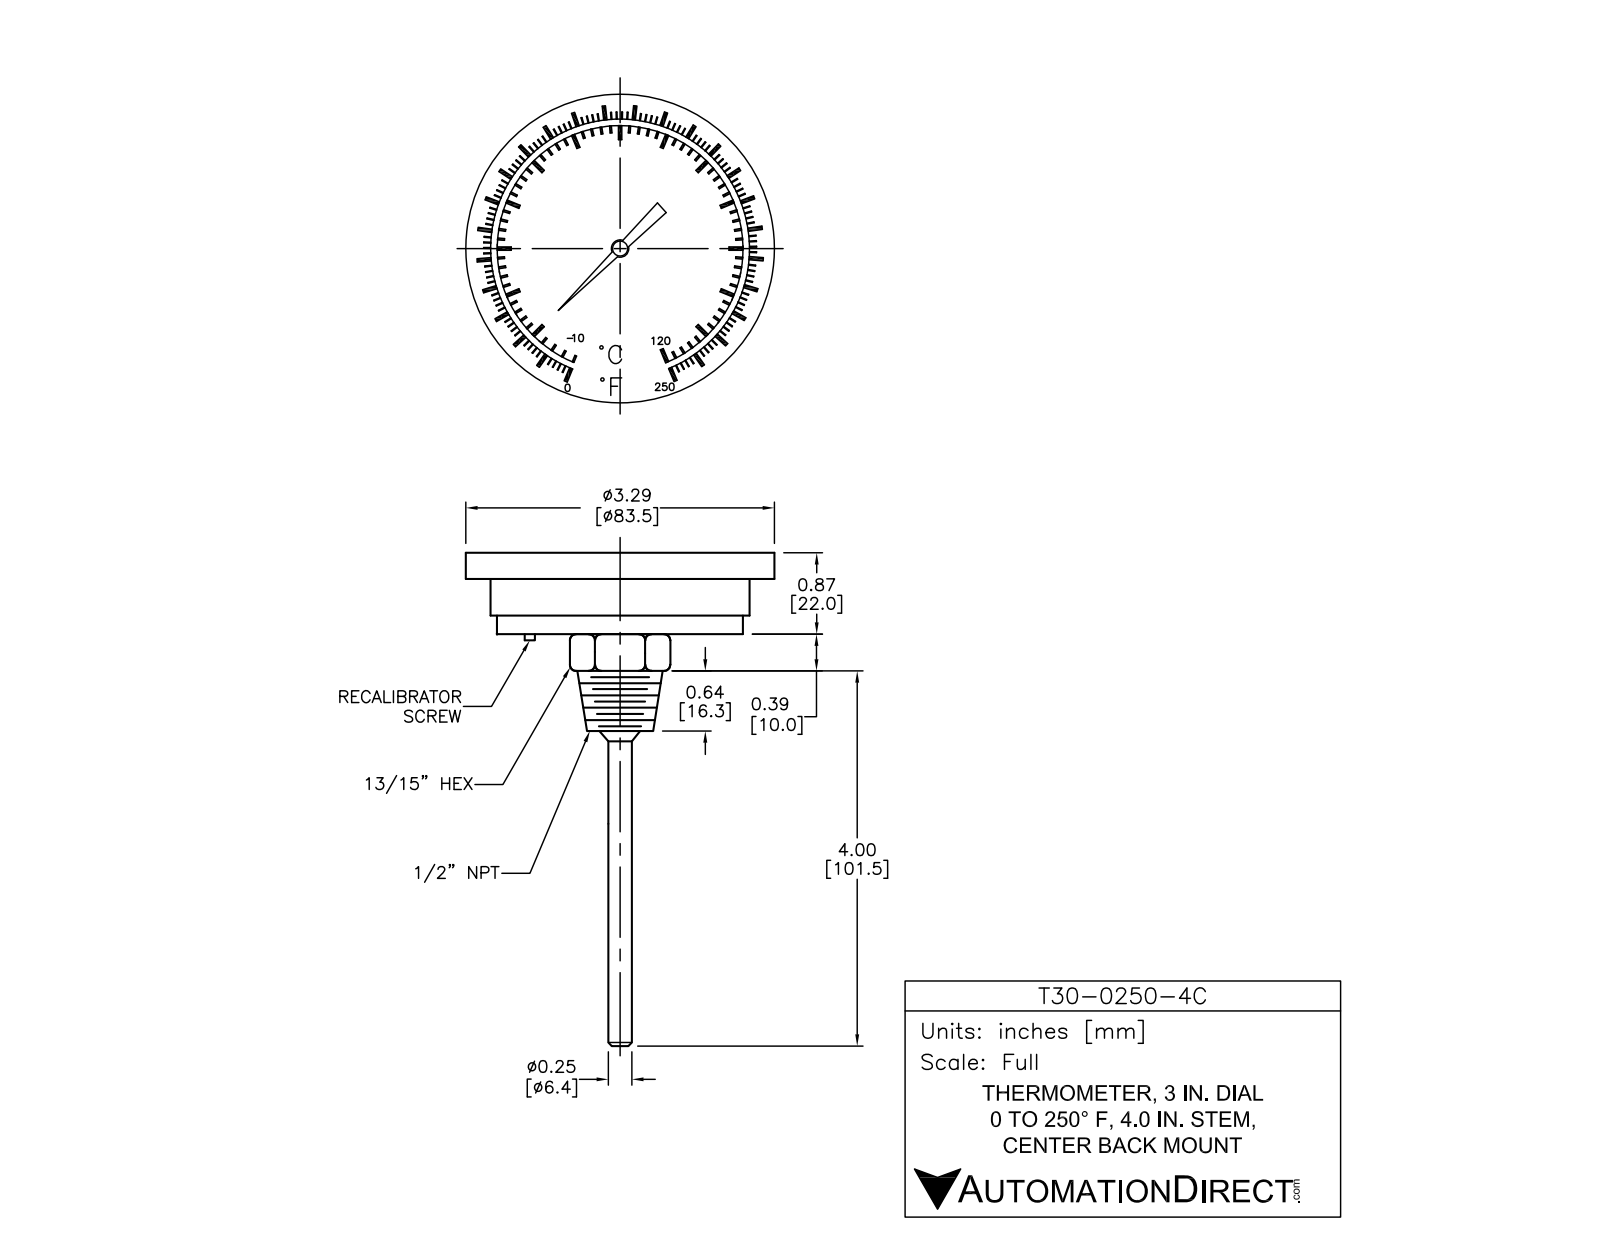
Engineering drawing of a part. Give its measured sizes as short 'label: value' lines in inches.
name: T30-0250-4C
written by: SolidWorks 2021 (AUTOMOTIVE_DESIGN)
unit: in
bodies: 73 solids, 1252 faces (1096 planar, 85 cylindrical, 71 other)
size: 5.26 × 3.29 × 3.29
volume: 3.153 in³; area: 34.25 in²
holes: 1× ⌀0.067, 1× ⌀2.69
bosses: 1× ⌀3.29, 1× ⌀2.76, 1× ⌀2.62, 1× ⌀0.848, 1× ⌀0.258
rounds: 1× R0.04, 1× R0.709, 1× R0.859, 1× R0.969, 1× R1.119
face distances: 0.222, 0.078, 0.3, 0.87, 0.648, 0.57, 0.59, 0.368, 0.29, 0.28
